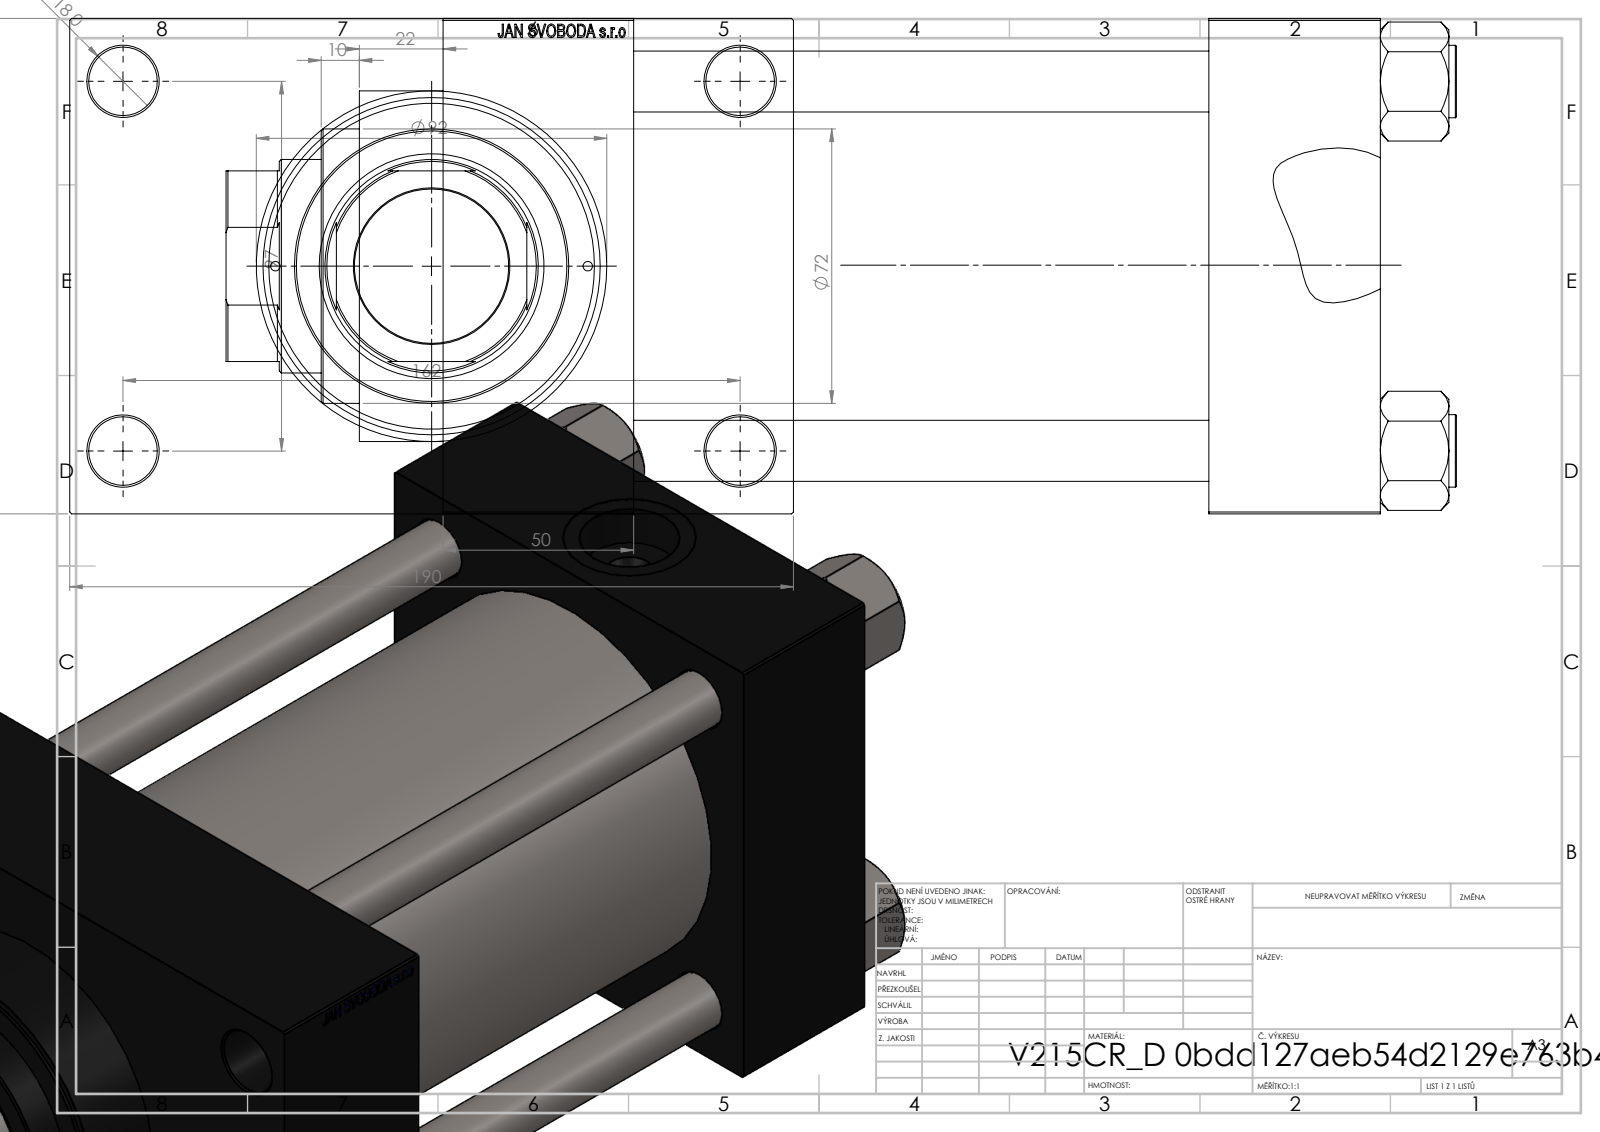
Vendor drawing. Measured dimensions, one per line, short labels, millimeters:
name: V215CR_D_TYCINKA; V215CR_D_Body; V215_VC_A; V215CR_VCP_D (+1 more)
written by: SolidWorks 2019 (CONFIG_CONTROL_DESIGN)
unit: mm
bodies: 11 solids, 1160 faces (547 planar, 93 cylindrical, 520 other)
size: 323 × 190 × 130
volume: 2 983 000 mm³; area: 441 658 mm²
holes: 4× ⌀16, 4× ⌀18, 2× ⌀2.5, 2× ⌀7, 2× ⌀26.44, 2× ⌀35, 1× ⌀40.5, 1× ⌀56, 1× ⌀59, 1× ⌀76, 1× ⌀85.5, 1× ⌀100
bosses: 4× ⌀19, 1× ⌀106, 1× ⌀92, 1× ⌀72
rounds: 1× R27
face distances: 130, 50, 45, 196, 151, 246, 201, 30, 160, 190
hole spacings: 32.55, 49.02, 62.87, 68.52, 94.41, 96.9, 101.73, 102.27
